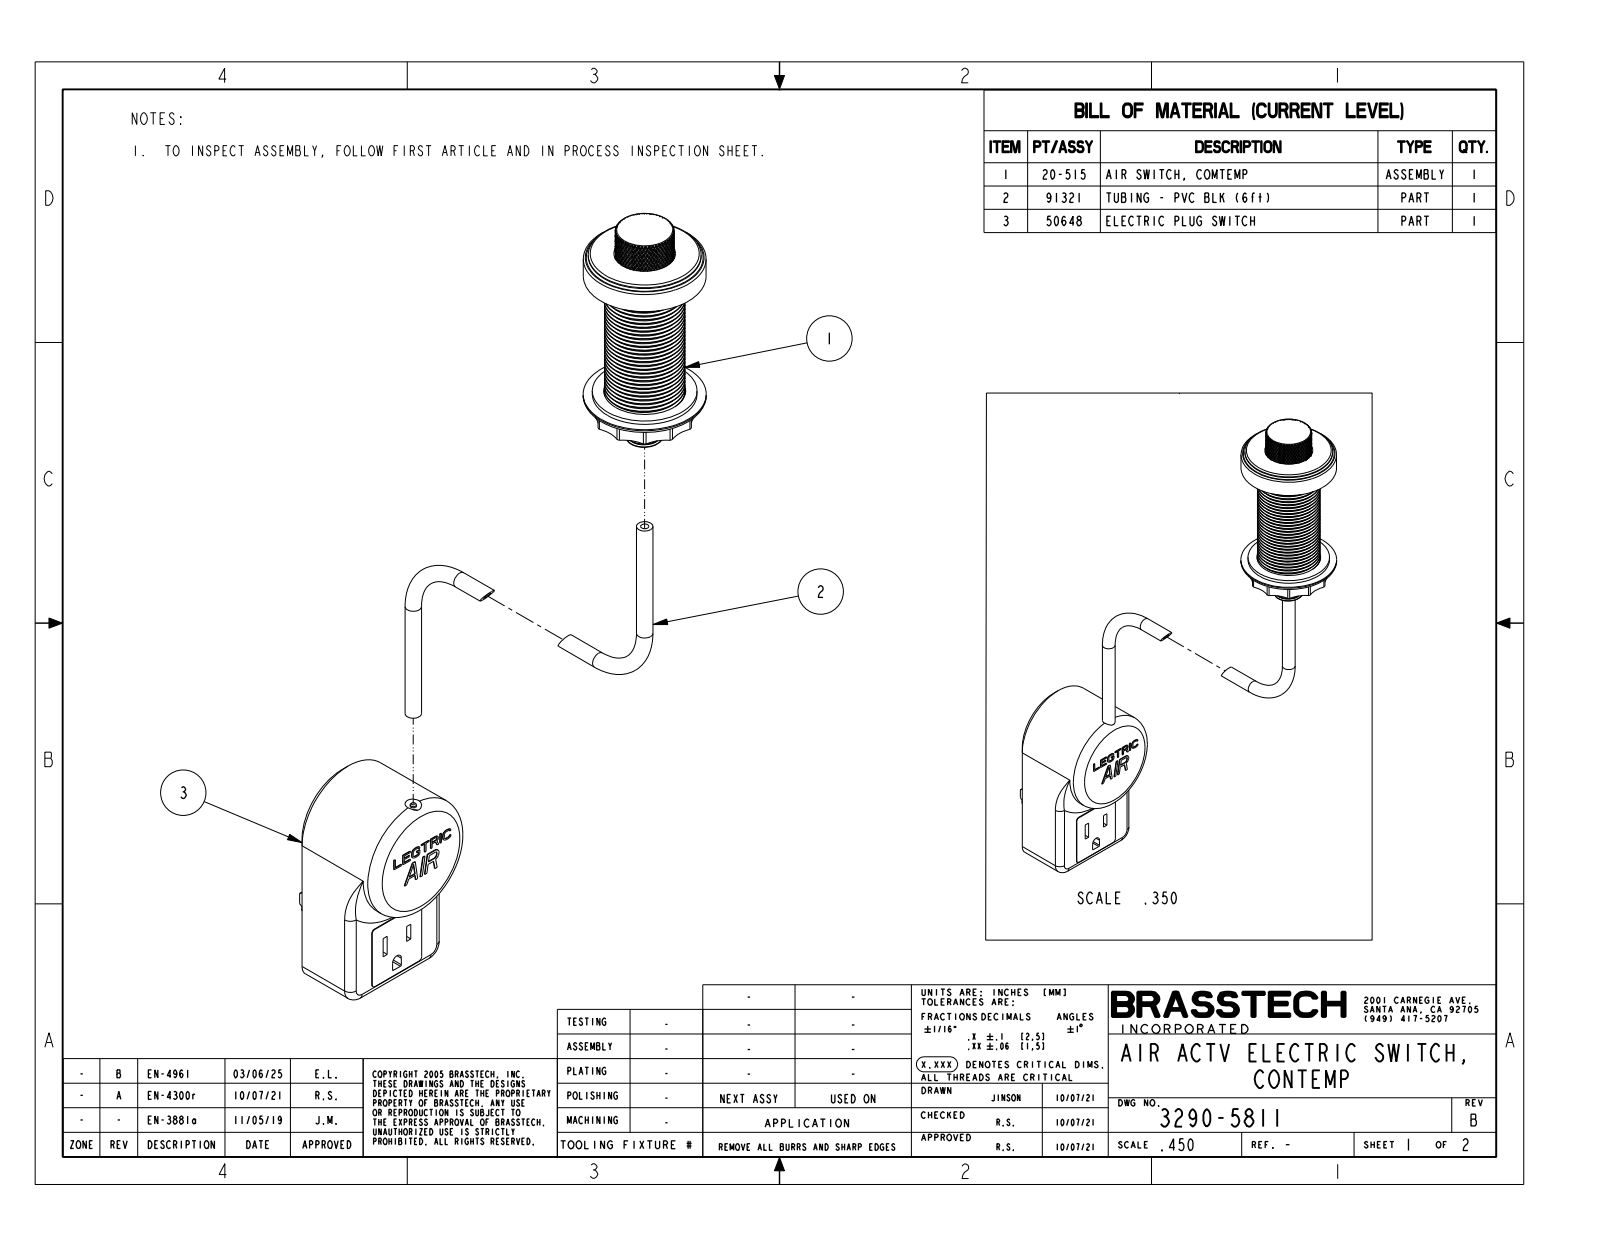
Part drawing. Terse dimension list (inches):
name: 3290-5811
written by: CREO PARAMETRIC BY PTC INC, 2023134 (CONFIG_CONTROL_DESIGN)
unit: in
bodies: 3 solids, 3812 faces (261 planar, 762 cylindrical, 2789 other)
size: 12.984 × 8.313 × 1.99
volume: 14.19 in³; area: 75.01 in²
holes: 4× ⌀0.125, 1× ⌀0.08, 1× ⌀0.35, 1× ⌀0.94, 1× ⌀1.25
bosses: 3× ⌀0.25, 1× ⌀1.99, 1× ⌀1.88, 1× ⌀1.875, 1× ⌀1.725, 1× ⌀1.6, 1× ⌀1.23, 1× ⌀1.153
rounds: 12× R0.5, 4× R0.06, 3× R0.125, 2× R0.02, 2× R0.25, 1× R0.095, 1× R0.81
face distances: 1.99, 1.7, 0.08, 0.425, 12.059, 12.484, 0.52, 0.36, 1.18, 1.17
hole spacings: 5
